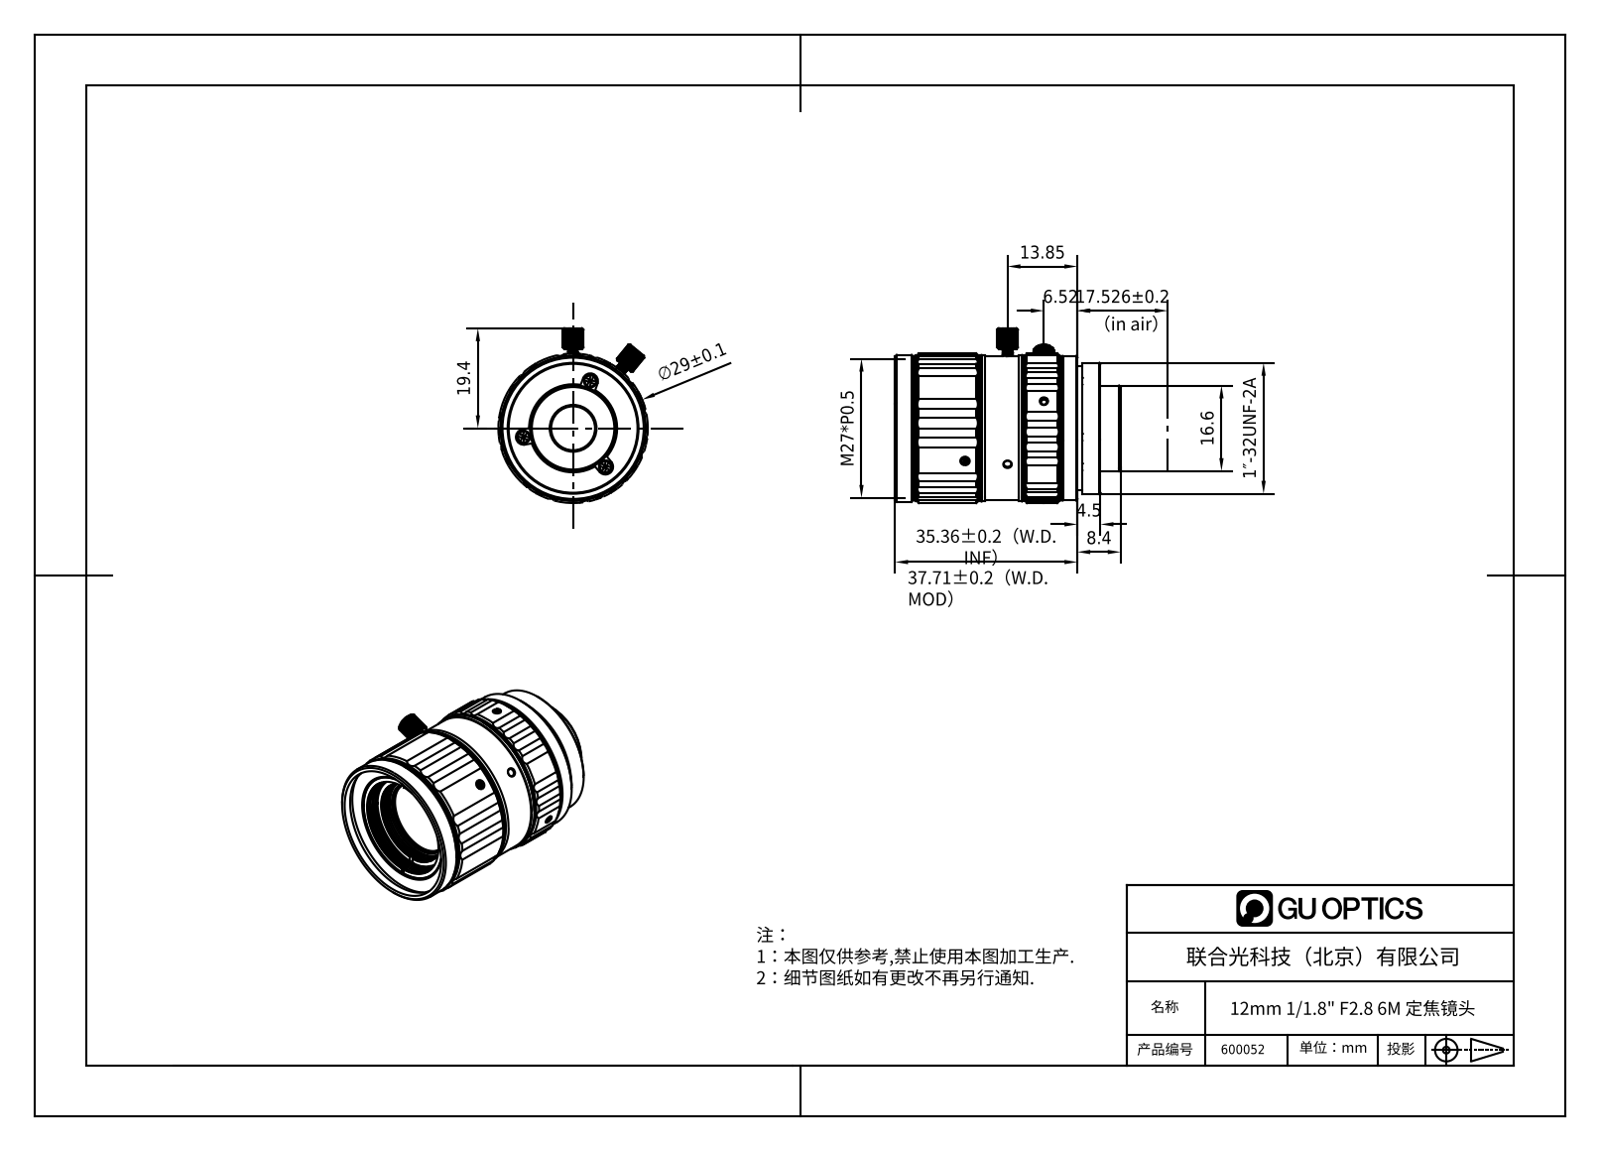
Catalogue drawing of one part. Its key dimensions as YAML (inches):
part_name: "600052"
step_written_by: "SolidWorks 2020 (CONFIG_CONTROL_DESIGN)"
units: inches
bodies: {solids: 11, faces: 1119, planar: 280, cylindrical: 555, other: 284}
overall_size: [1.723, 1.321, 1.141]
volume: 1.389
surface_area: 14.34
round_holes:
  - {diameter: 0.048, count: 6}
  - {diameter: 0.063, count: 4}
  - {diameter: 0.047, count: 3}
  - {diameter: 0.057, count: 3}
  - {diameter: 0.067, count: 3}
  - {diameter: 0.064, count: 1}
  - {diameter: 0.335, count: 1}
  - {diameter: 0.421, count: 1}
  - {diameter: 0.509, count: 1}
  - {diameter: 0.547, count: 1}
  - {diameter: 0.567, count: 1}
  - {diameter: 0.591, count: 1}
round_bosses_or_shafts:
  - {diameter: 0.063, count: 8}
  - {diameter: 0.098, count: 3}
  - {diameter: 0.047, count: 3}
  - {diameter: 0.047, count: 3}
  - {diameter: 0.079, count: 2}
  - {diameter: 1.142, count: 1}
  - {diameter: 1.122, count: 1}
  - {diameter: 1.118, count: 1}
partial_cylinders:
  - {radius: 0.059, count: 27}
  - {radius: 0.091, count: 18}
  - {radius: 0.135, count: 6}
  - {radius: 0.044, count: 5}
  - {radius: 0.133, count: 4}
  - {radius: 0.044, count: 2}
  - {radius: 0.079, count: 2}
  - {radius: 0.031, count: 1}
face_to_face_distances: [0.039, 1.431, 1.471, 1.294, 1.585, 1.067, 1.244, 0.227, 0.187, 0.331]
hole_center_spacings: [0.384, 0.665, 0.665, 0.383]
